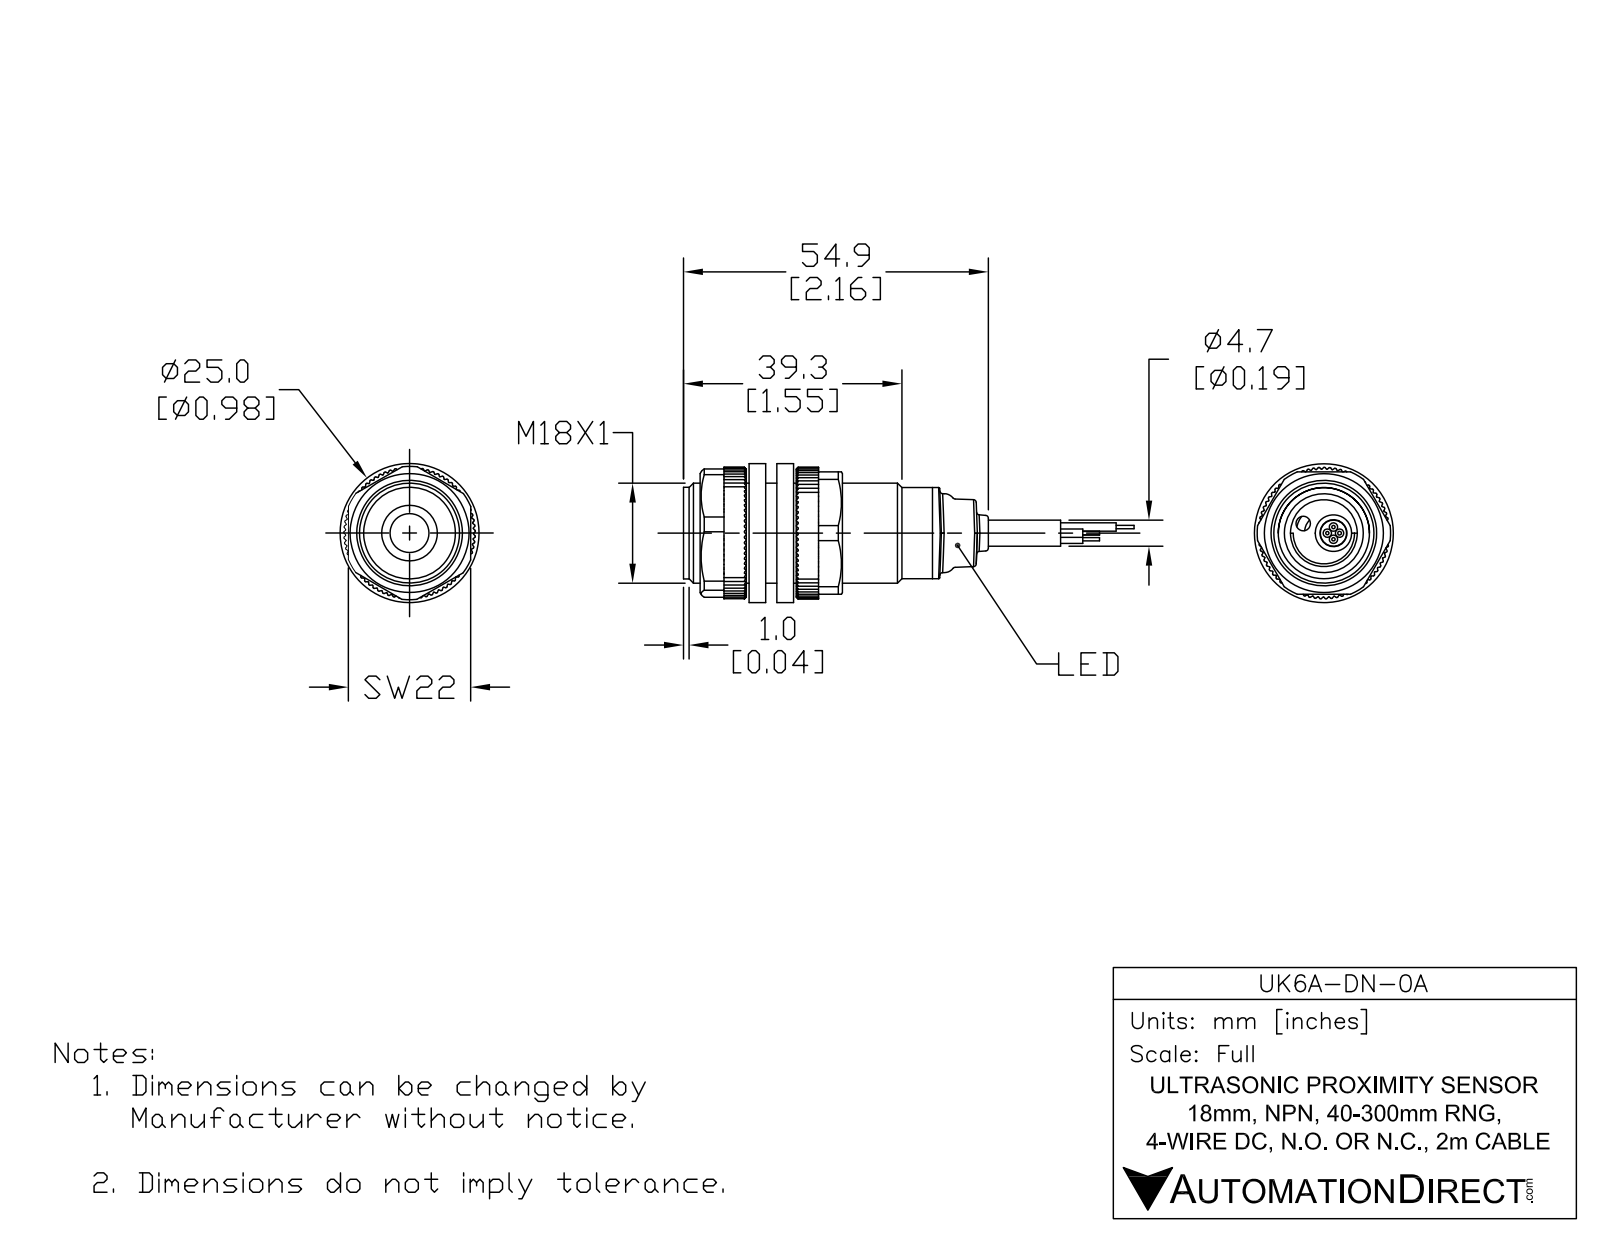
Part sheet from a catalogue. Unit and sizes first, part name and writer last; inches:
Units: inches
Overall size (bounding box): 3.537 × 0.709 × 0.709
Round holes (diameter × count): ⌀0.185 ×1, ⌀0.374 ×1
Round bosses / shafts (diameter × count): ⌀0.709 ×1, ⌀0.646 ×1, ⌀0.622 ×1, ⌀0.559 ×1
Partial cylindrical surfaces — rounded edges, fillets, slot ends (radius × count): R0.008 ×1, R0.02 ×1
Main face-to-face distances: 1.724, 0.039, 1.764, 0.039, 1.763, 1.963, 1.962, 1.923, 0.199, 0.255
Hole centre spacings: 0.068
Volume: 0.787 in³ · Surface area: 7.432 in²
Bodies: 4 solids, 62 faces (14 planar, 19 cylindrical, 29 other)
Part name (STEP PRODUCT): UK6A-DN-0A
STEP written by: SolidWorks 2017 (AUTOMOTIVE_DESIGN)
